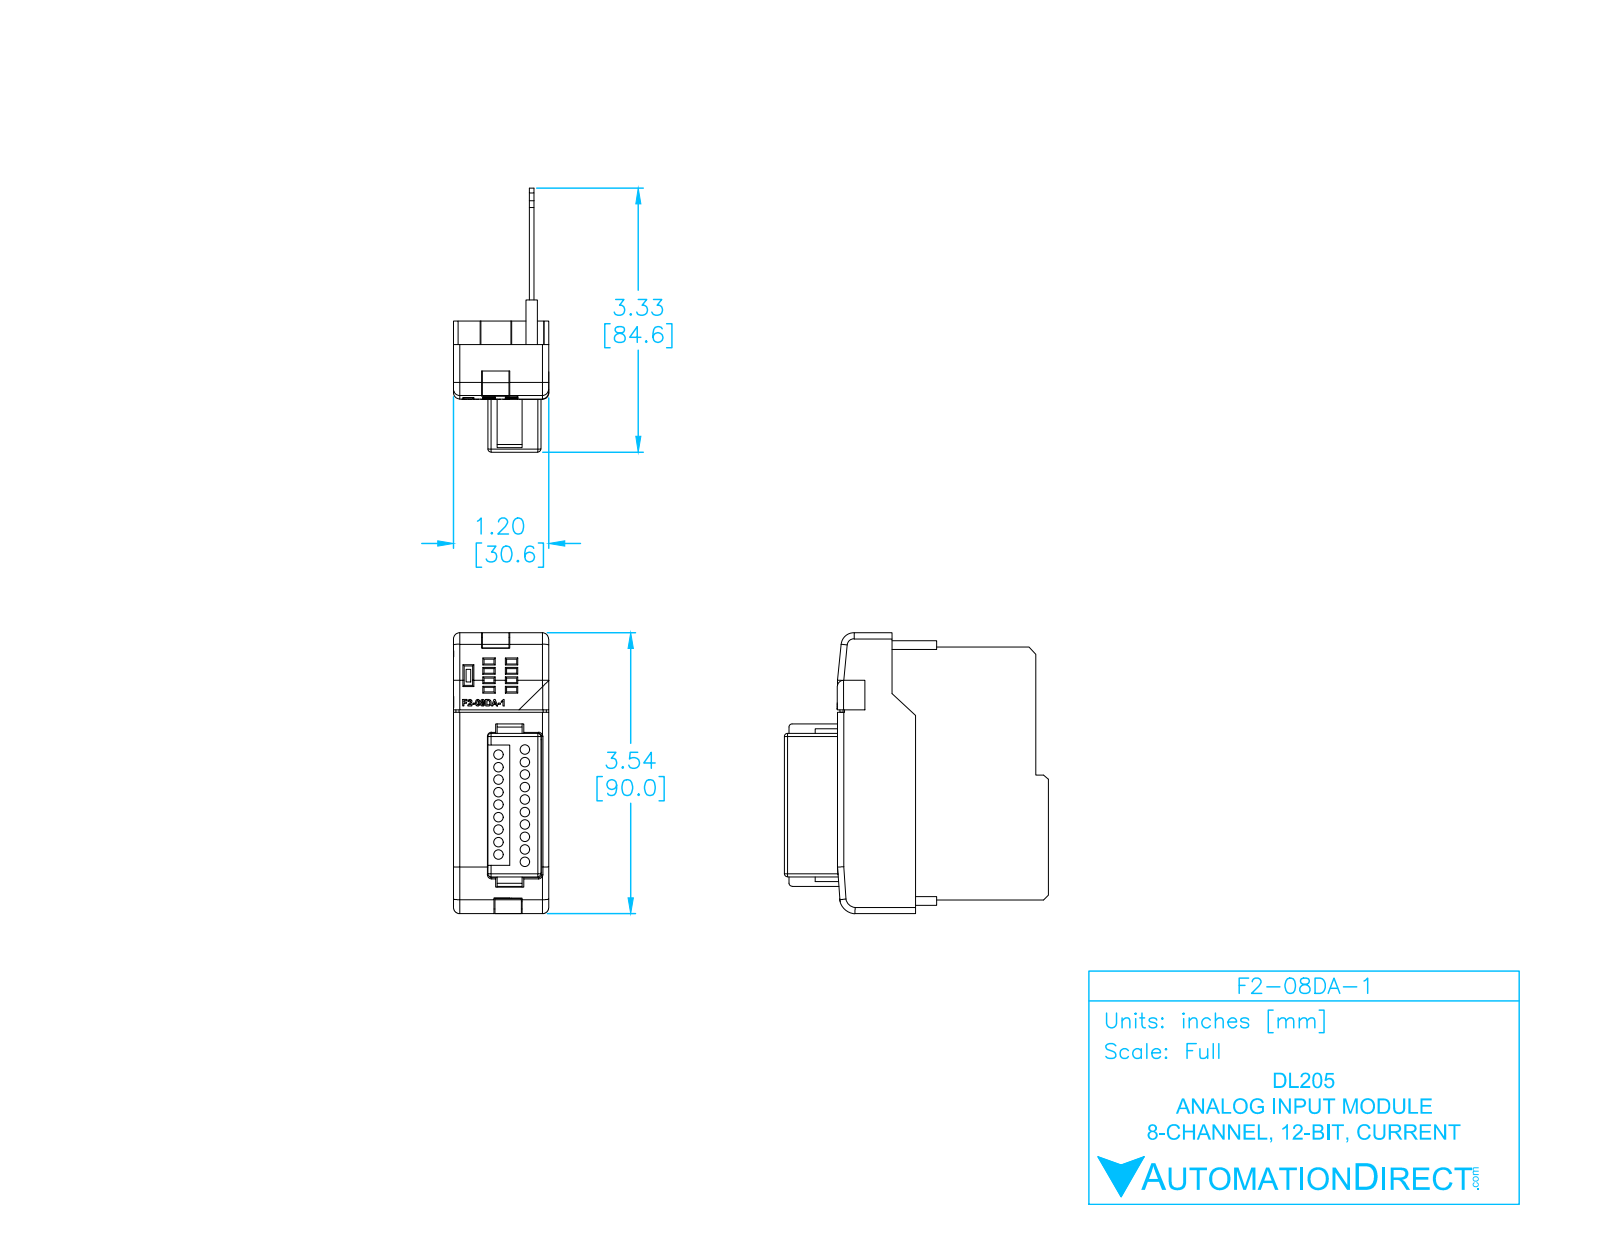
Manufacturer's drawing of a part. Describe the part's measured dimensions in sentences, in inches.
The part is named "F2-08DA-1_ModuleCase Light_NEW". Its 3-D file was written by "SolidWorks 2009 (AUTOMOTIVE_DESIGN)". It is 2 solids with 638 faces: 410 planar, 158 cylindrical and 70 other. Overall it measures 3.543 by 3.331 by 1.203 inches. Its volume is 1.865 cubic inches and its surface area 50.54 square inches. Round holes: 19 of diameter 0.118. Partial cylindrical surfaces (rounded edges, fillets, slot ends): 28 of radius 0.014, 18 of radius 0.039, 12 of radius 0.02, 11 of radius 0.079, 6 of radius 0.01, 1 of radius 0.103, 1 of radius 0.149, 1 of radius 0.162. The main face-to-face distances are 0.059, 0.186, 0.127, 0.245, 0.02, 0.039, 0.956, 1.142, 0.709, 0.433. The hole center spacings are 0.157, 0.315, 0.472, 0.63, 0.339, 0.345, 0.787, 0.4.
